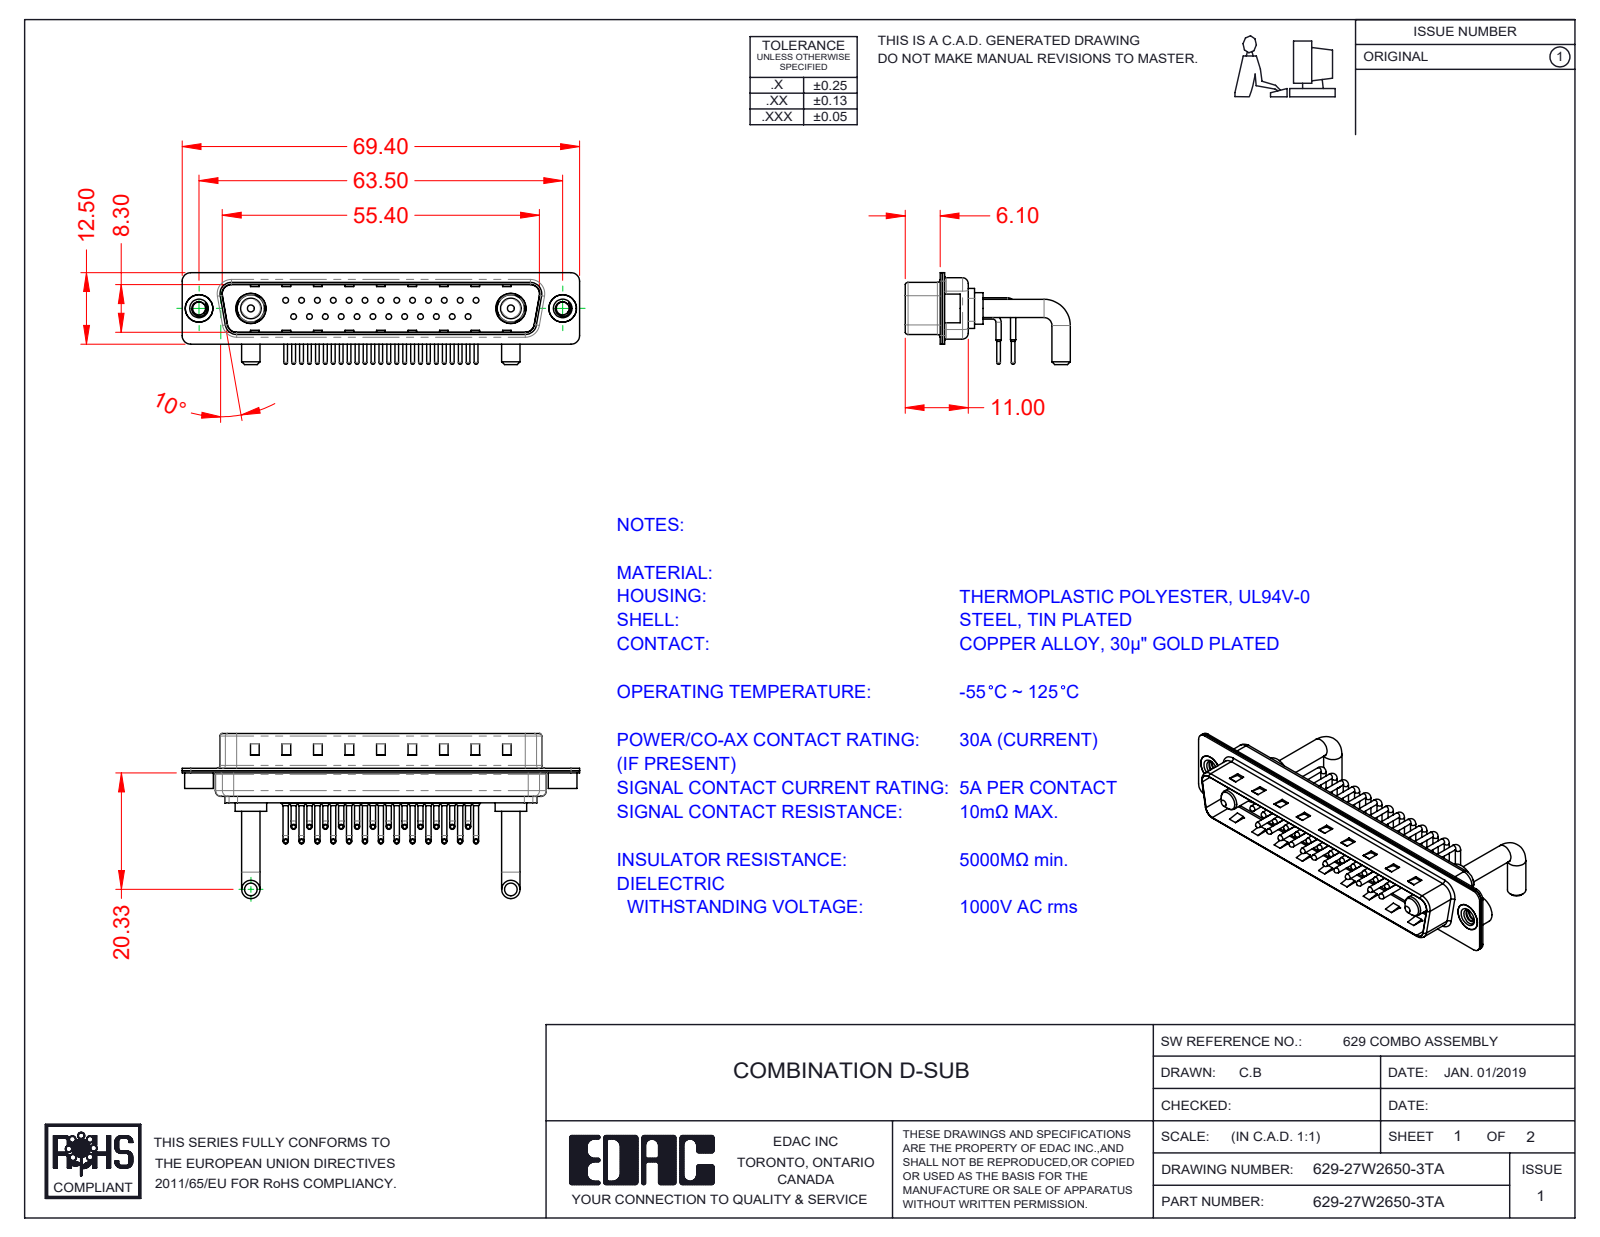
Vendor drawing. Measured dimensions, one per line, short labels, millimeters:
name: 629Combo Housing_27W2; 629Combo Shell Rear_37 Contacts; 629Combo Threaded Rivet_2; 629Combo Contact Row 2 (+4 more)
written by: SolidWorks 2020 (CONFIG_CONTROL_DESIGN)
unit: mm
bodies: 34 solids, 3248 faces (1823 planar, 1083 cylindrical, 342 other)
size: 69.4 × 28.83 × 16.05
volume: 4 410 mm³; area: 10 282 mm²
holes: 25× ⌀0.75, 25× ⌀1.6, 25× ⌀2, 2× ⌀2.26, 2× ⌀4, 2× ⌀4.8, 2× ⌀4.85, 2× ⌀5.3
bosses: 50× ⌀0.9, 25× ⌀1.5, 25× ⌀1, 25× ⌀0.65, 4× ⌀3.2, 2× ⌀5.5, 2× ⌀5.2, 2× ⌀5
rounds: 25× R1.01, 16× R1.5, 12× R2, 8× R0.5, 8× R1.6, 4× R0.25, 4× R0.6, 4× R0.65
face distances: 0.4, 0.8, 9.5, 9.1, 8.7, 9.9, 0.75, 5.6, 1.2, 0.35
hole spacings: 3.16, 2.77, 5.54, 8.31, 5.03, 7.48, 11.08, 5.04
